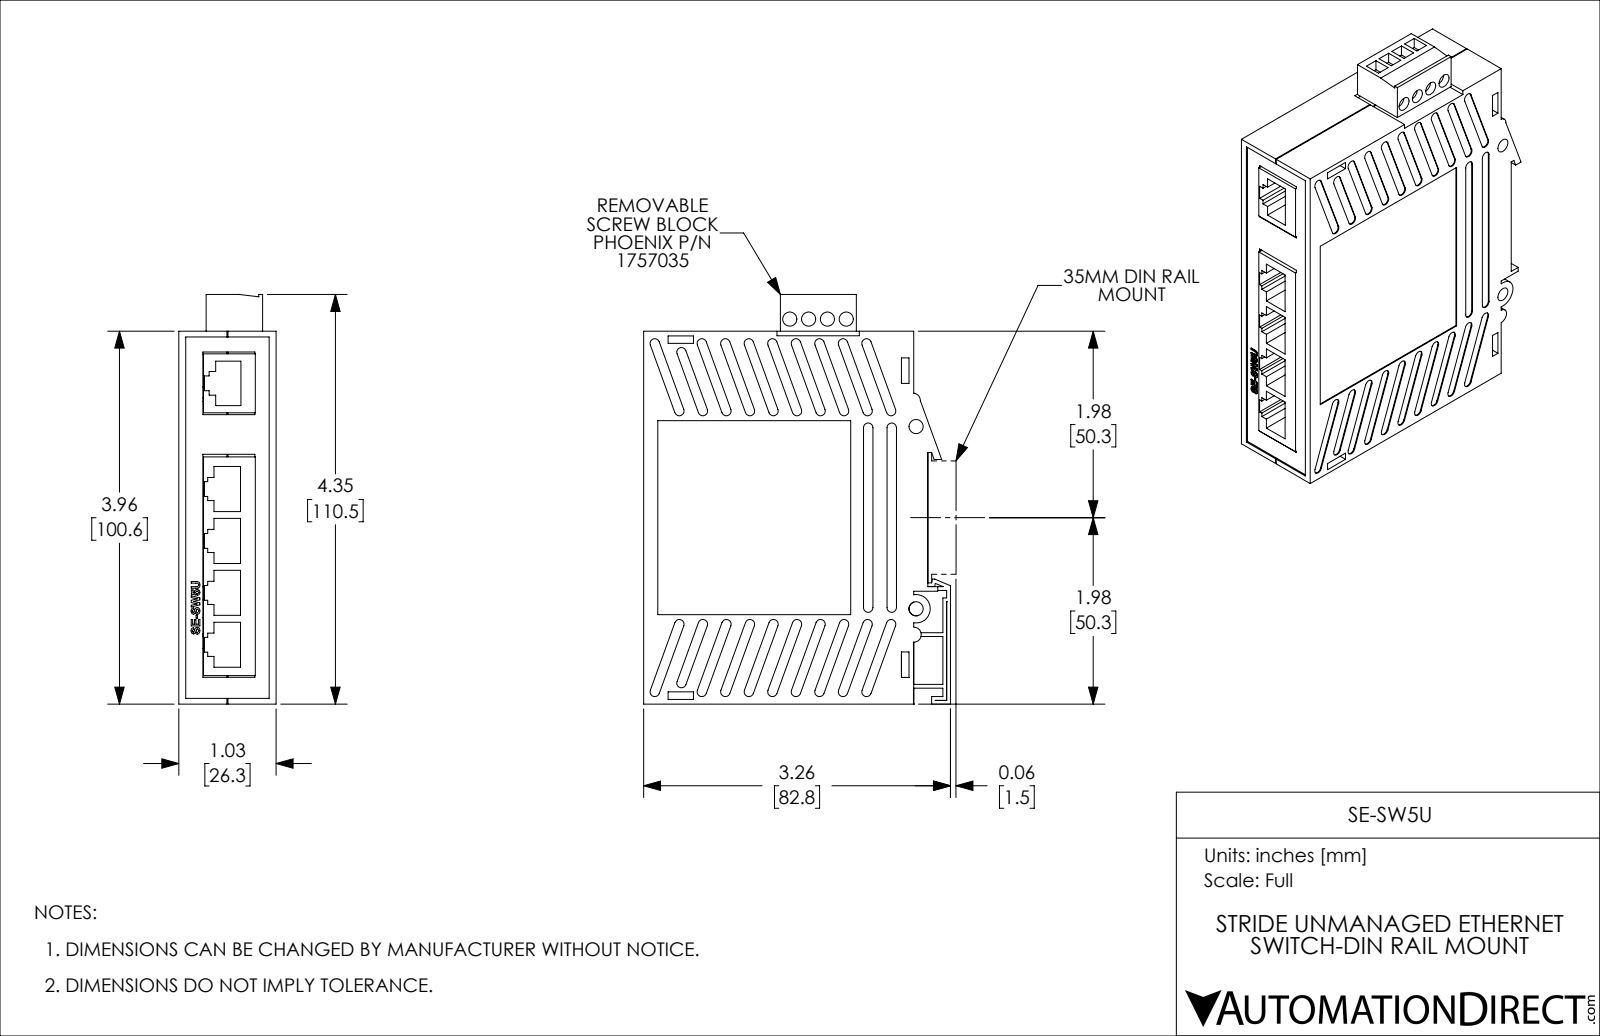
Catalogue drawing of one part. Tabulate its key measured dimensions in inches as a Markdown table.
| quantity | value |
| --- | --- |
| part name | SE-SW5U |
| STEP written by | SolidWorks 2019 (AUTOMOTIVE_DESIGN) |
| units | inches |
| bodies | 17 solids, 1069 faces (669 planar, 355 cylindrical, 45 other) |
| overall size | 4.35 × 3.26 × 1.033 |
| volume | 2.477 in³ |
| surface area | 101 in² |
| round holes (diameter × count) | 0.15 × 6, 0.081 × 1 |
| round bosses / shafts (diameter × count) | 0.229 × 1 |
| partial cylindrical surfaces (radius × count) | 0.05 × 44, 0.089 × 44, 0.04 × 1, 0.041 × 1, 0.044 × 1, 0.08 × 1, 0.08 × 1, 0.081 × 1 |
| main face-to-face distances | 0.039, 0.984, 0.974, 0.049, 1.024, 0.935, 1.014, 1.033, 0.945, 0.994 |
| hole center spacings | 0.2, 0.4, 0.276, 0.6, 1.361, 1.48, 1.615, 1.761 |
